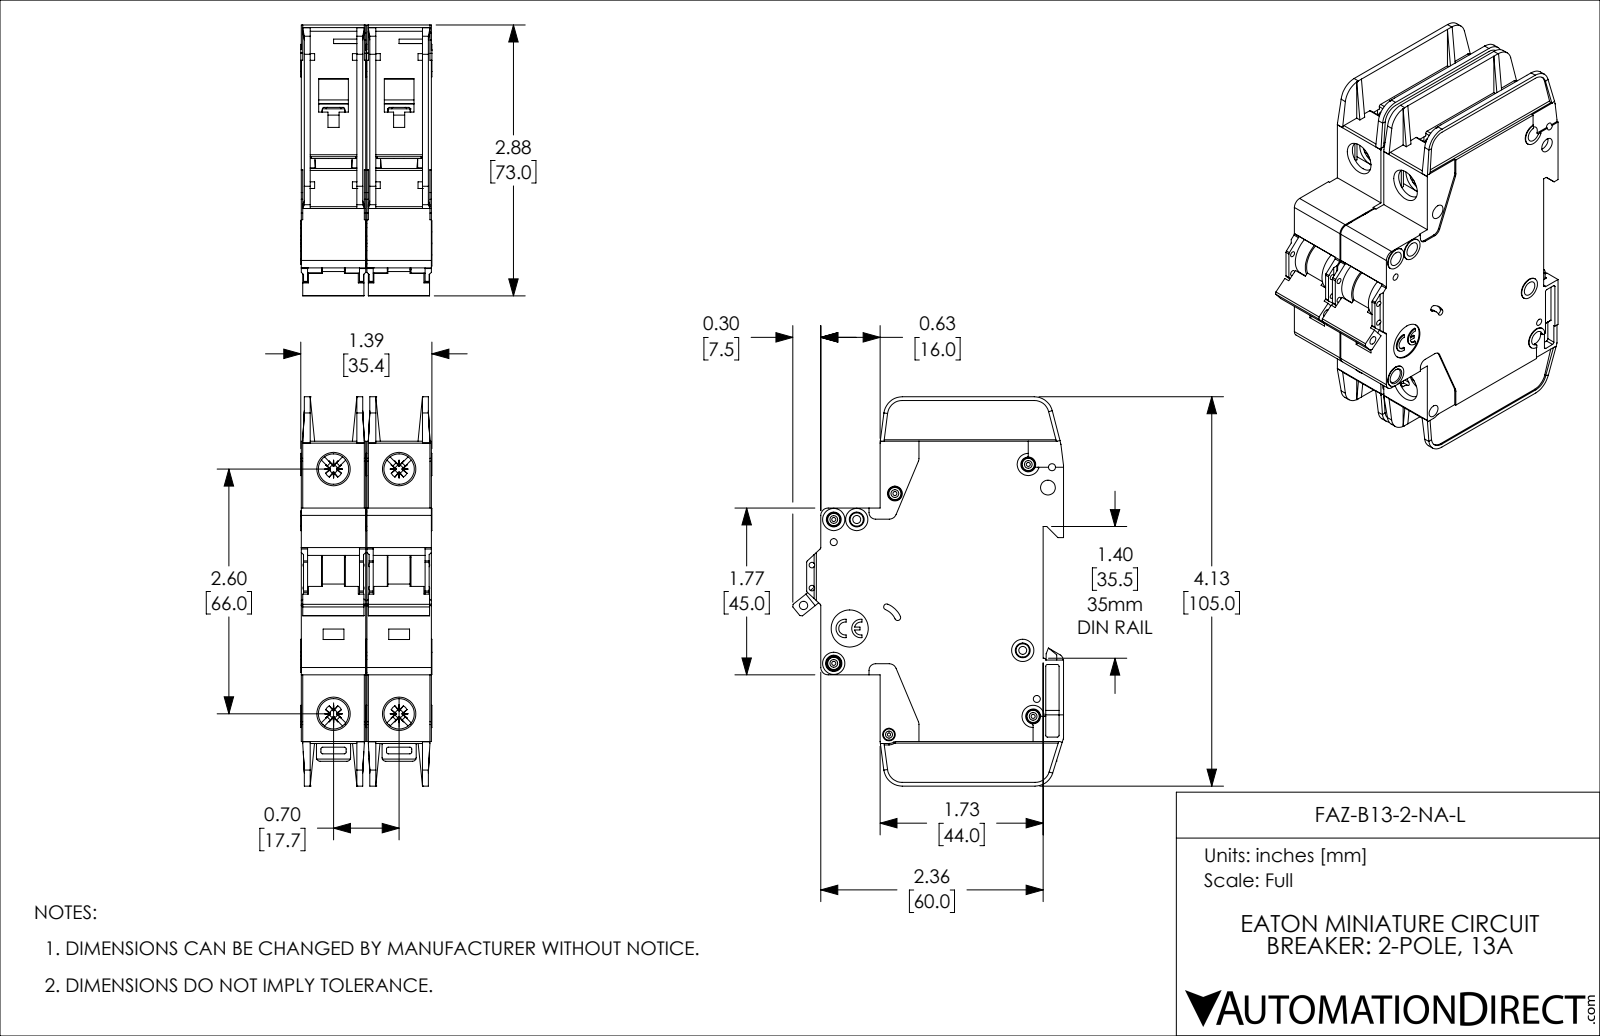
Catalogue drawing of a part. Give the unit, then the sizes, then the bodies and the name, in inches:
Units: inches
Overall size (bounding box): 4.134 × 2.876 × 1.394
Round holes (diameter × count): ⌀0.157 ×8, ⌀0.043 ×5, ⌀0.075 ×4, ⌀0.323 ×4, ⌀0.059 ×2, ⌀0.085 ×2, ⌀0.035 ×1, ⌀0.089 ×1, ⌀0.098 ×1, ⌀0.134 ×1, ⌀0.394 ×1
Round bosses / shafts (diameter × count): ⌀0.13 ×5, ⌀0.236 ×4, ⌀0.118 ×3, ⌀0.098 ×2
Partial cylindrical surfaces — rounded edges, fillets, slot ends (radius × count): R0.02 ×57, R0.016 ×20, R0.039 ×14, R0.079 ×10, R0.043 ×8, R0.008 ×5, R0.197 ×5, R0.01 ×4
Main face-to-face distances: 0.697, 0.047, 0.685, 0.591, 0.094, 0.638, 0.543, 1.382, 0.744, 0.65
Hole centre spacings: 0.244, 0.537, 0.697, 0.87, 2.598, 2.69, 0.189, 0.199
Volume: 9.365 in³ · Surface area: 82.01 in²
Bodies: 2 solids, 2254 faces (1342 planar, 714 cylindrical, 198 other)
Part name (STEP PRODUCT): FAZ-B13-2-NA-L
STEP written by: SolidWorks 2019 (AUTOMOTIVE_DESIGN)
